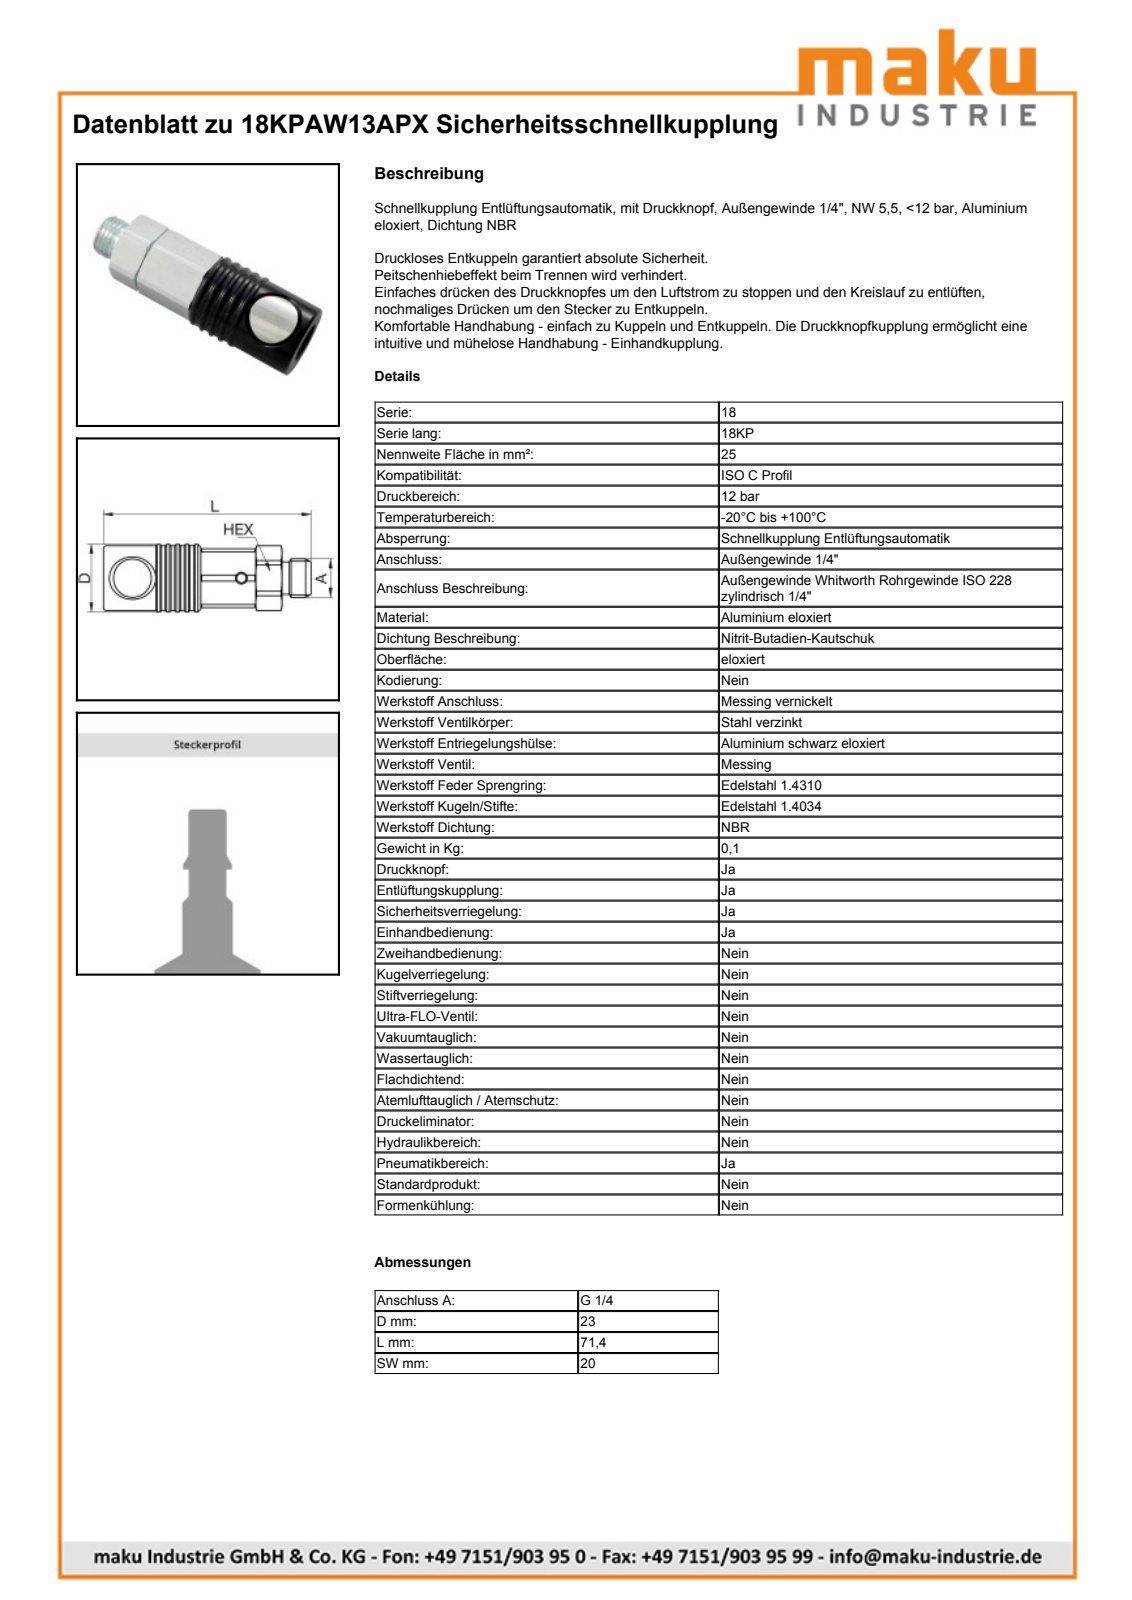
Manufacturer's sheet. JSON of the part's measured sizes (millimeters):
{"part_name": "18KPAW13APX", "step_written_by": "Autodesk Inventor 2019 (CONFIG_CONTROL_DESIGN)", "units": "millimeters", "bodies": {"solids": 27, "faces": 303, "planar": 96, "cylindrical": 105, "other": 102}, "overall_size": [71.4, 23, 23], "volume_mm3": 30679, "surface_area_mm2": 19750, "round_holes": [[2.5, 1], [3.5, 1], [5.5, 1], [7, 1], [8.5, 1], [9, 1], [10.1, 1], [10.4, 1], [10.5, 1], [11.1, 1], [12.9, 1], [14.05, 1]], "round_bosses_or_shafts": [[23, 1], [22, 1], [20, 1], [18.5, 1], [18.2, 1], [18, 1], [17.02, 1], [15.8, 1]], "partial_cylinders_radius": [[3.77, 1], [7.22, 1], [7.8, 1], [11, 1], [12.36, 1]], "face_to_face_distances": [20, 29.4, 52.4, 19, 10, 23, 11, 4.5, 7, 39.4], "hole_center_spacings": [1.2, 1.25, 37.43]}
